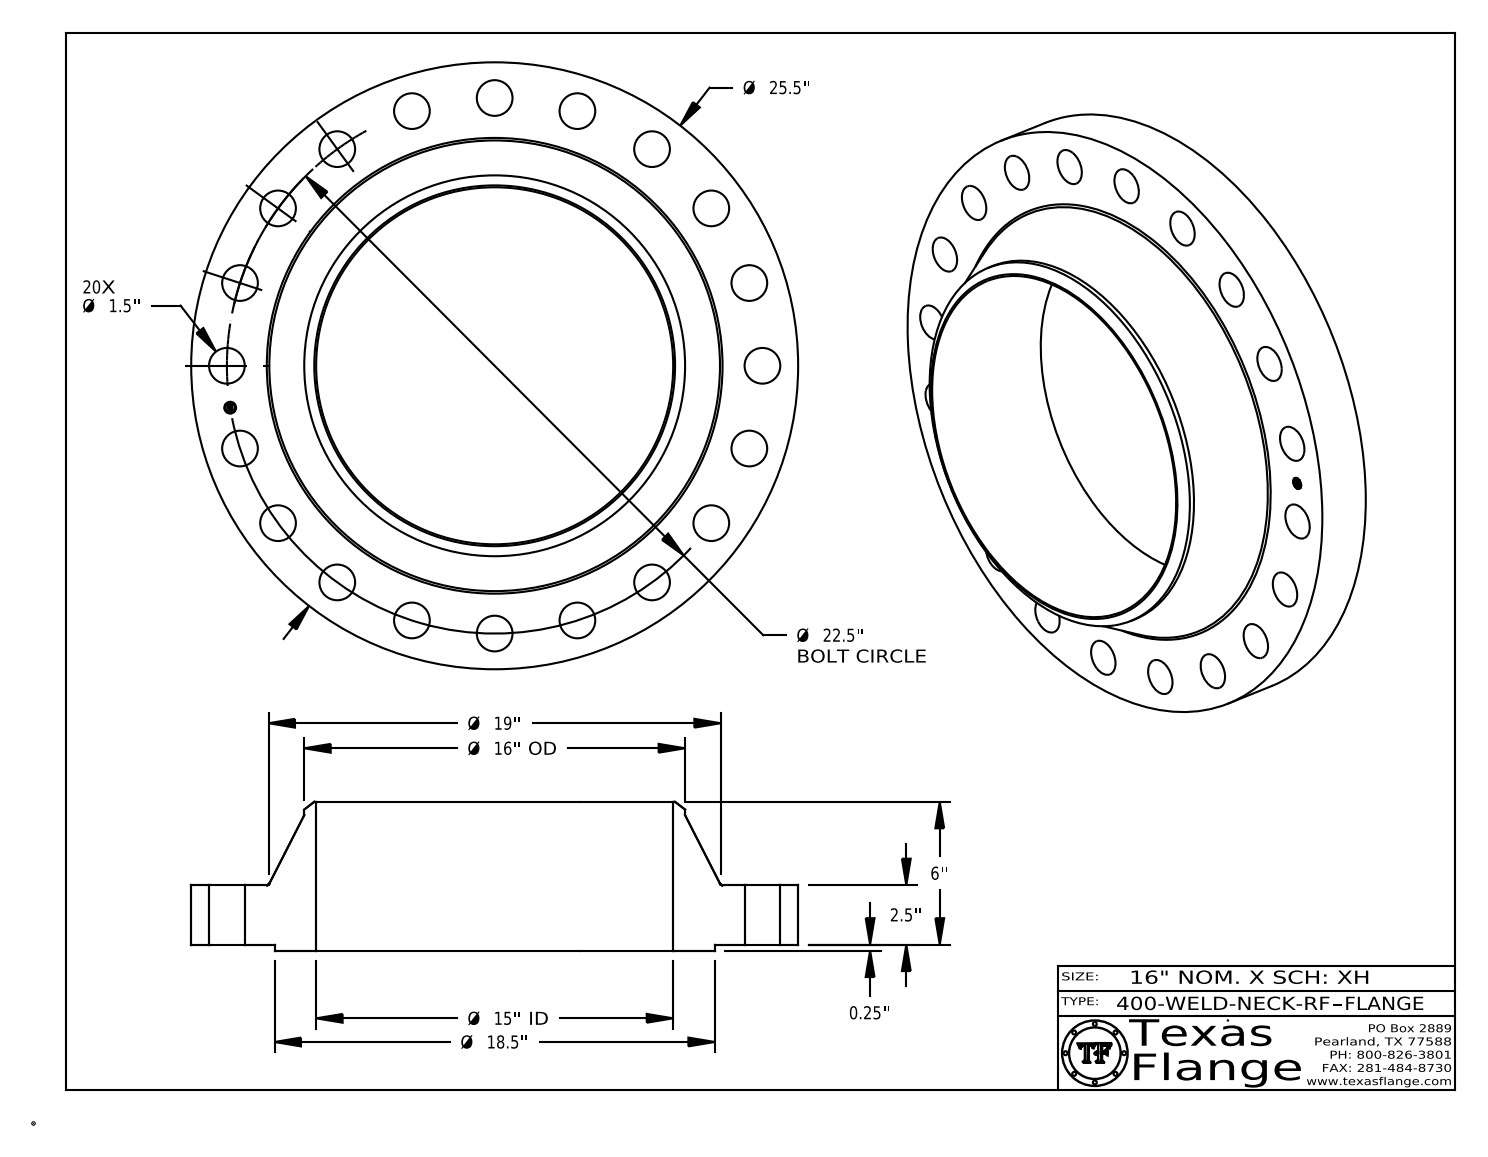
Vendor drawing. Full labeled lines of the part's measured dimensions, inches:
Part name (STEP PRODUCT): 400-WELD-NECK-RF
STEP written by: CATIA V5 STEP AP214 (AUTOMOTIVE_DESIGN)
Units: inches
Bodies: 1 solid, 443 faces (369 planar, 68 cylindrical, 6 other)
Overall size (bounding box): 25.5 × 25.5 × 6.25
Volume: 969.3 in³ · Surface area: 1 458 in²
Round holes (diameter × count): ⌀1.5 ×20, ⌀0.495 ×1, ⌀15 ×1
Round bosses / shafts (diameter × count): ⌀0.03 ×8, ⌀25.5 ×1, ⌀18.5 ×1, ⌀16 ×1, ⌀0.39 ×1
Main face-to-face distances: 2.5, 0.25, 2.75, 6.25, 6, 3.5, 2.735, 2.485, 0.015, 3.515
Hole centre spacings: 11.25, 6.953, 13.225, 3.52, 18.203, 20.048, 21.399, 22.223
